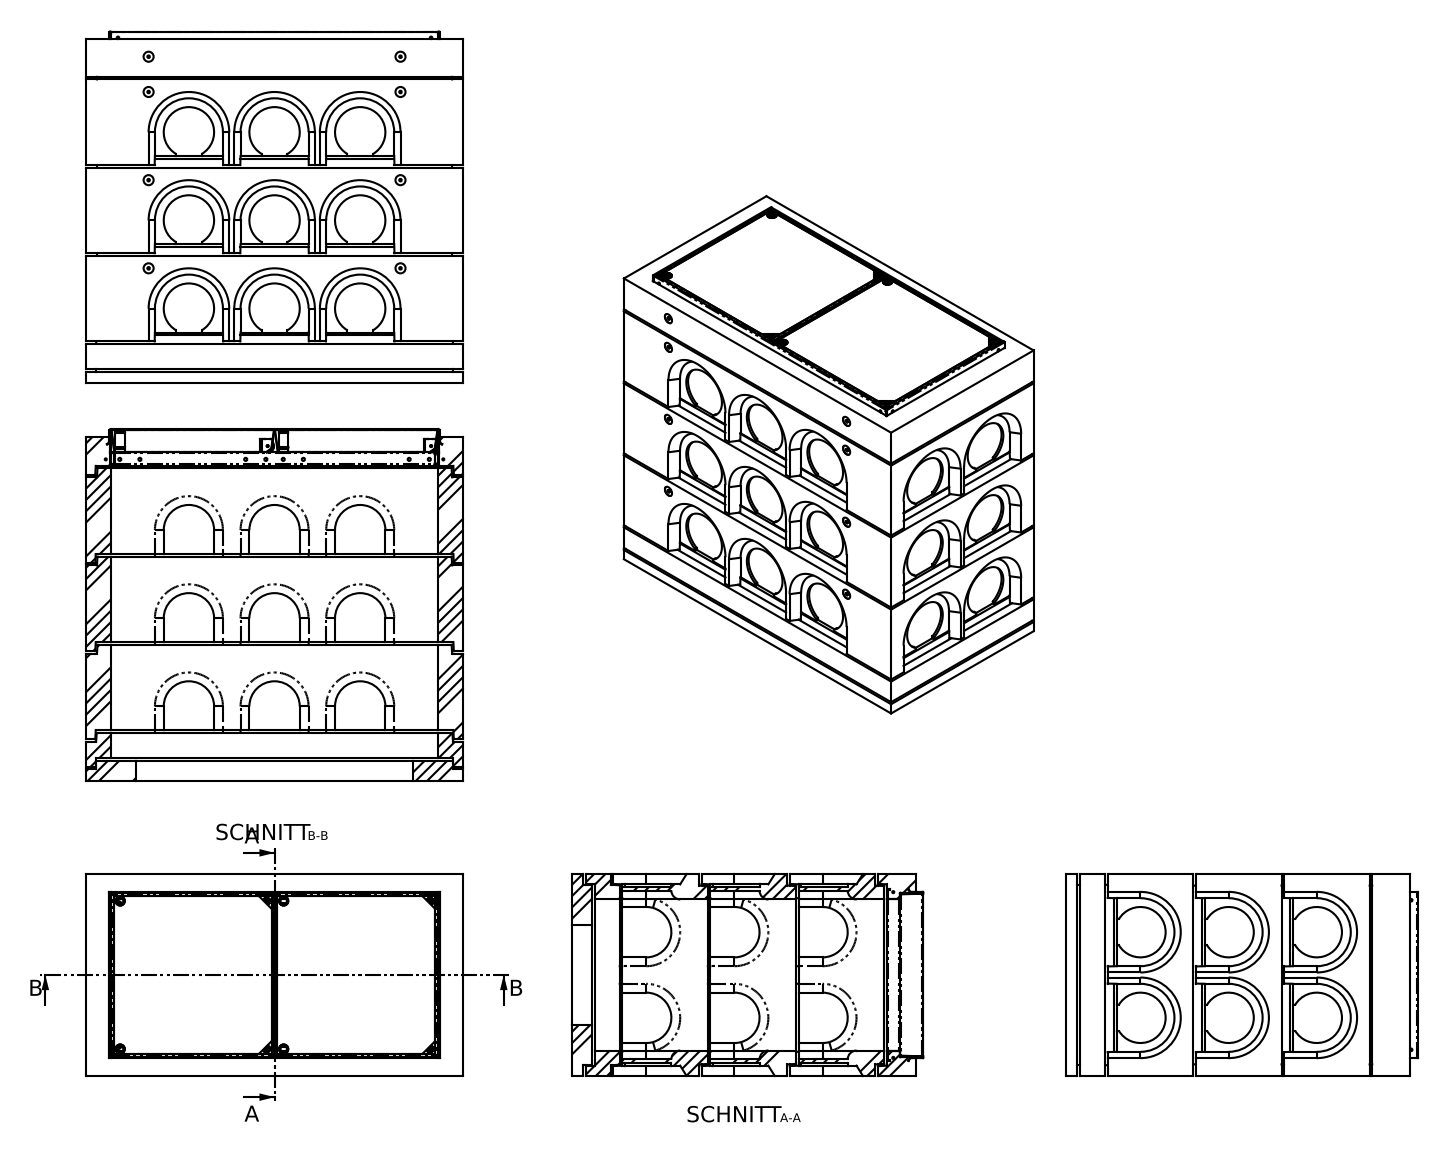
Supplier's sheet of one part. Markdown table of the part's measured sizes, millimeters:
| quantity | value |
| --- | --- |
| part name | SC-ECO.0613.133.125 |
| STEP written by | SolidWorks 2018 (AUTOMOTIVE_DESIGN) |
| units | millimeters |
| bodies | 0 solids, 606 faces (395 planar, 126 cylindrical, 85 other) |
| overall size | 1500 × 1395 × 800 |
| round holes (diameter × count) | 200 × 15, 10 × 4, 26.5 × 4, 35 × 4, 40 × 2 |
| round bosses / shafts (diameter × count) | 5.81 × 8, 10 × 6 |
| partial cylindrical surfaces (radius × count) | 35 × 20, 3 × 8, 2.5 × 6, 13.5 × 4 |
| main face-to-face distances | 700, 10, 50, 100, 350, 800, 35, 25, 315, 710 |
| hole center spacings | 487.95, 340, 350, 778.2, 700, 764.79, 680, 142.78 |
